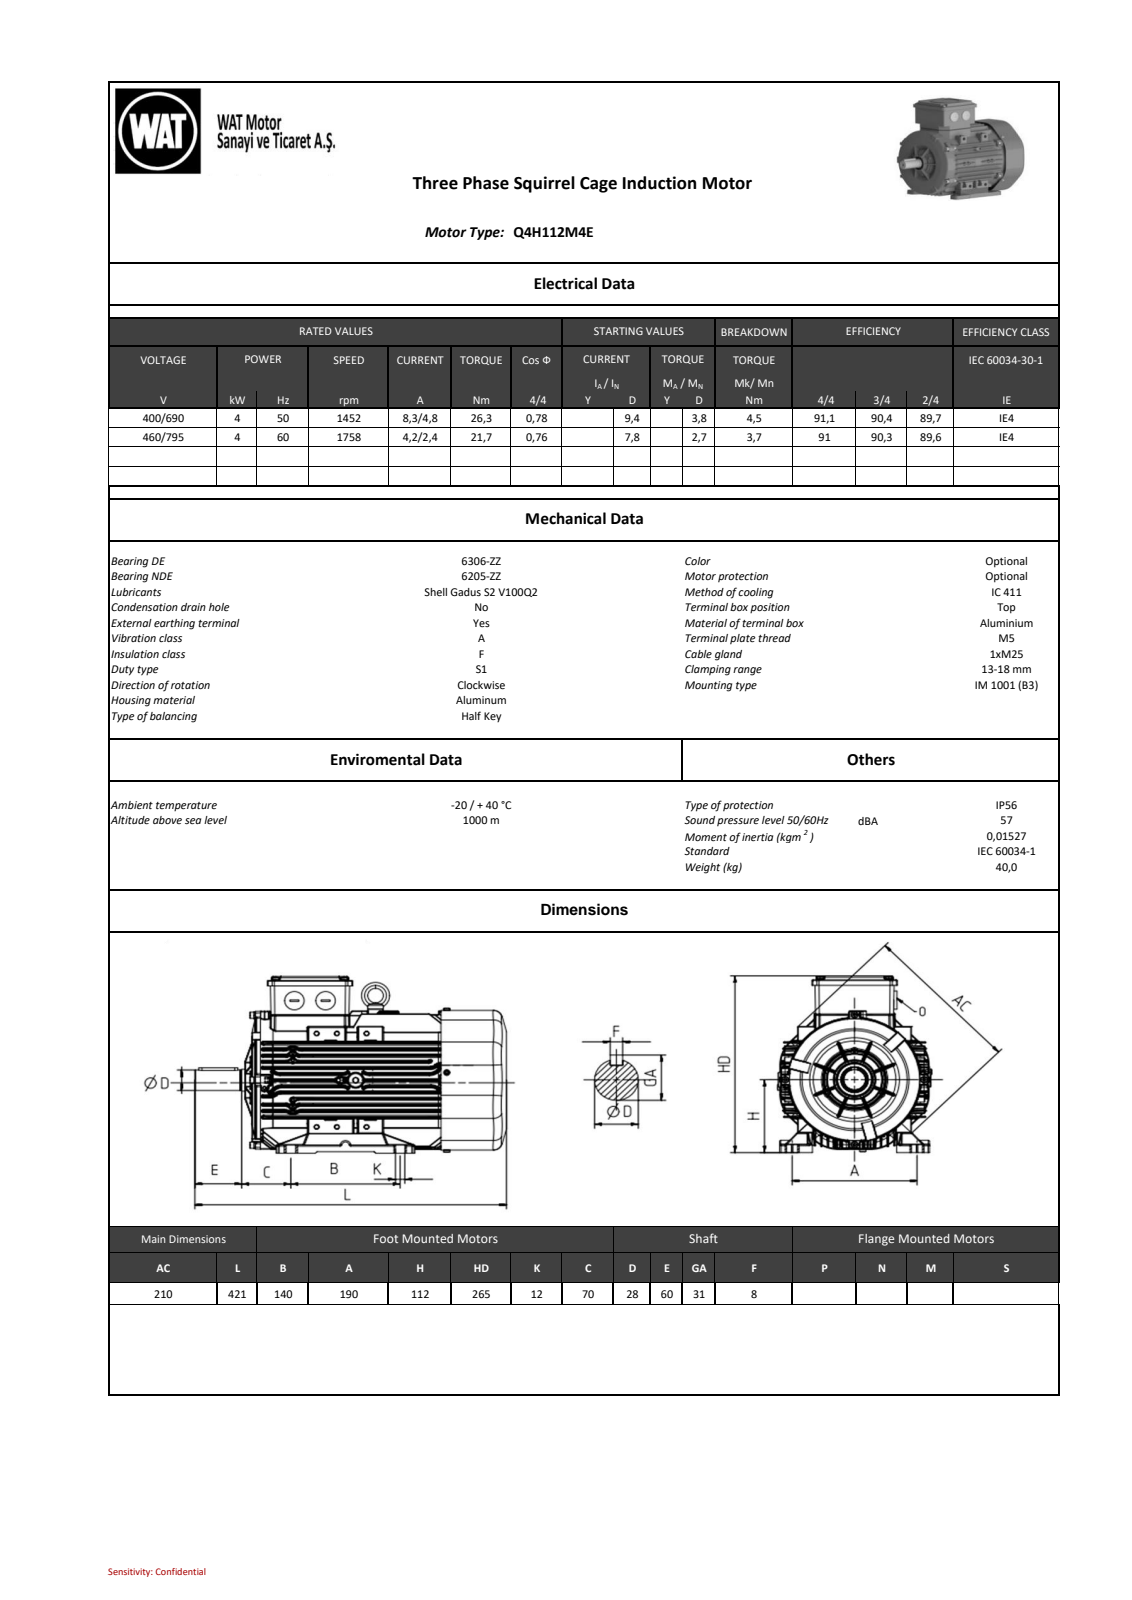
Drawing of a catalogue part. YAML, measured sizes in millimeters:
part_name: "QH series_ 112_B3 _DEEP COVER__stp_objects"
step_written_by: "SIEMENS PLM Software NX2206.8101 (AUTOMOTIVE_DESIGN)"
units: millimeters
bodies: {solids: 0, faces: 7578, planar: 1699, cylindrical: 2901, other: 2978}
overall_size: [421, 275.46, 225.11]
round_holes:
  - {diameter: 3.5, count: 4}
  - {diameter: 4.6, count: 2}
  - {diameter: 8, count: 1}
  - {diameter: 8.5, count: 1}
round_bosses_or_shafts:
  - {diameter: 14.8, count: 4}
  - {diameter: 13, count: 4}
  - {diameter: 10, count: 4}
  - {diameter: 8, count: 4}
  - {diameter: 25, count: 2}
  - {diameter: 6, count: 2}
  - {diameter: 188, count: 1}
  - {diameter: 35.83, count: 1}
partial_cylinders:
  - {radius: 2, count: 696}
  - {radius: 0.8, count: 602}
  - {radius: 1, count: 469}
  - {radius: 0.5, count: 259}
  - {radius: 3, count: 87}
  - {radius: 4, count: 12}
  - {radius: 6, count: 12}
  - {radius: 10, count: 10}
face_to_face_distances: [1, 21.5, 10.99, 35.96, 99.54, 24.97, 8.16, 112.88, 89.87, 90.43]
hole_center_spacings: [22.01]
